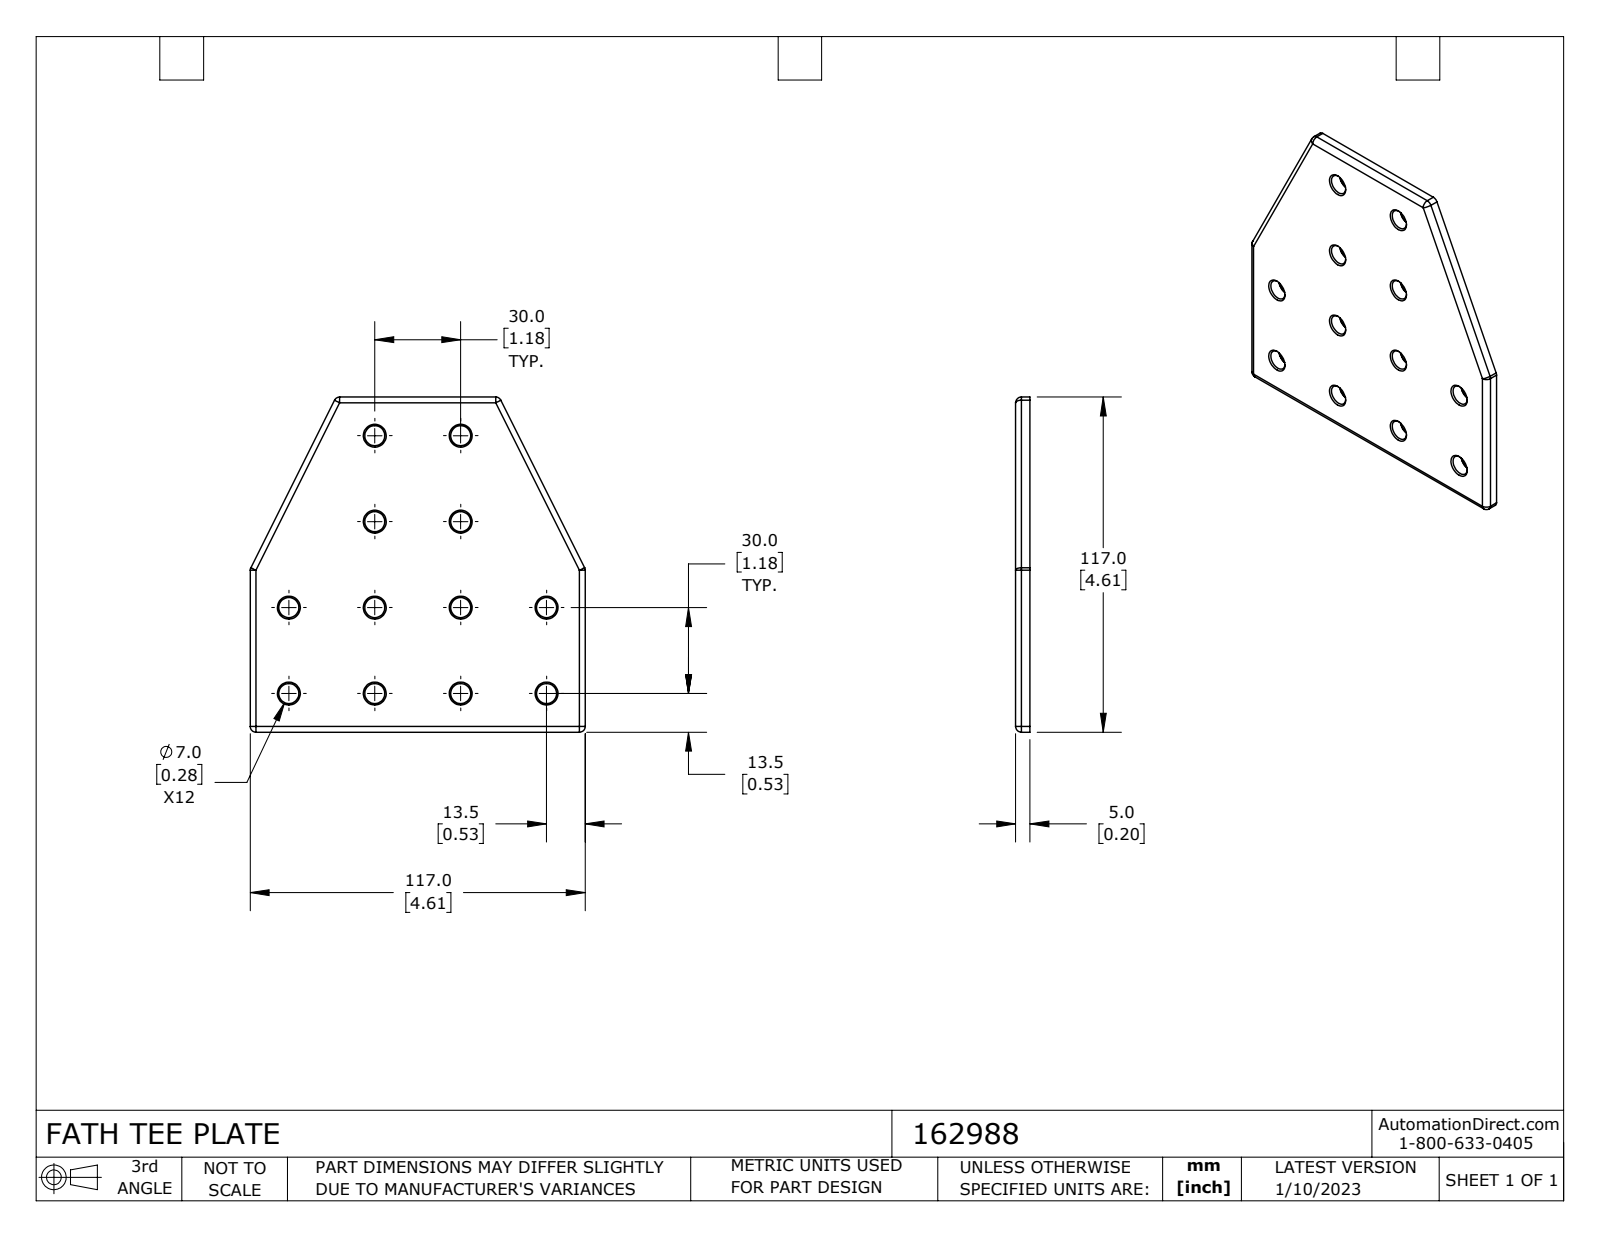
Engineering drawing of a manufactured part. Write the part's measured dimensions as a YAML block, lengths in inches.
part_name: "162988"
step_written_by: "SolidWorks 2021 (CONFIG_CONTROL_DESIGN)"
units: inches
bodies: {solids: 1, faces: 98, planar: 8, cylindrical: 36, other: 54}
overall_size: [4.606, 4.606, 0.197]
volume: 3.46
surface_area: 39.93
round_holes:
  - {diameter: 0.276, count: 12}
partial_cylinders:
  - {radius: 0.079, count: 12}
face_to_face_distances: [0.197, 4.606]
hole_center_spacings: [1.181, 2.641, 1.67, 2.362, 3.735, 3.341, 3.543, 4.259]
